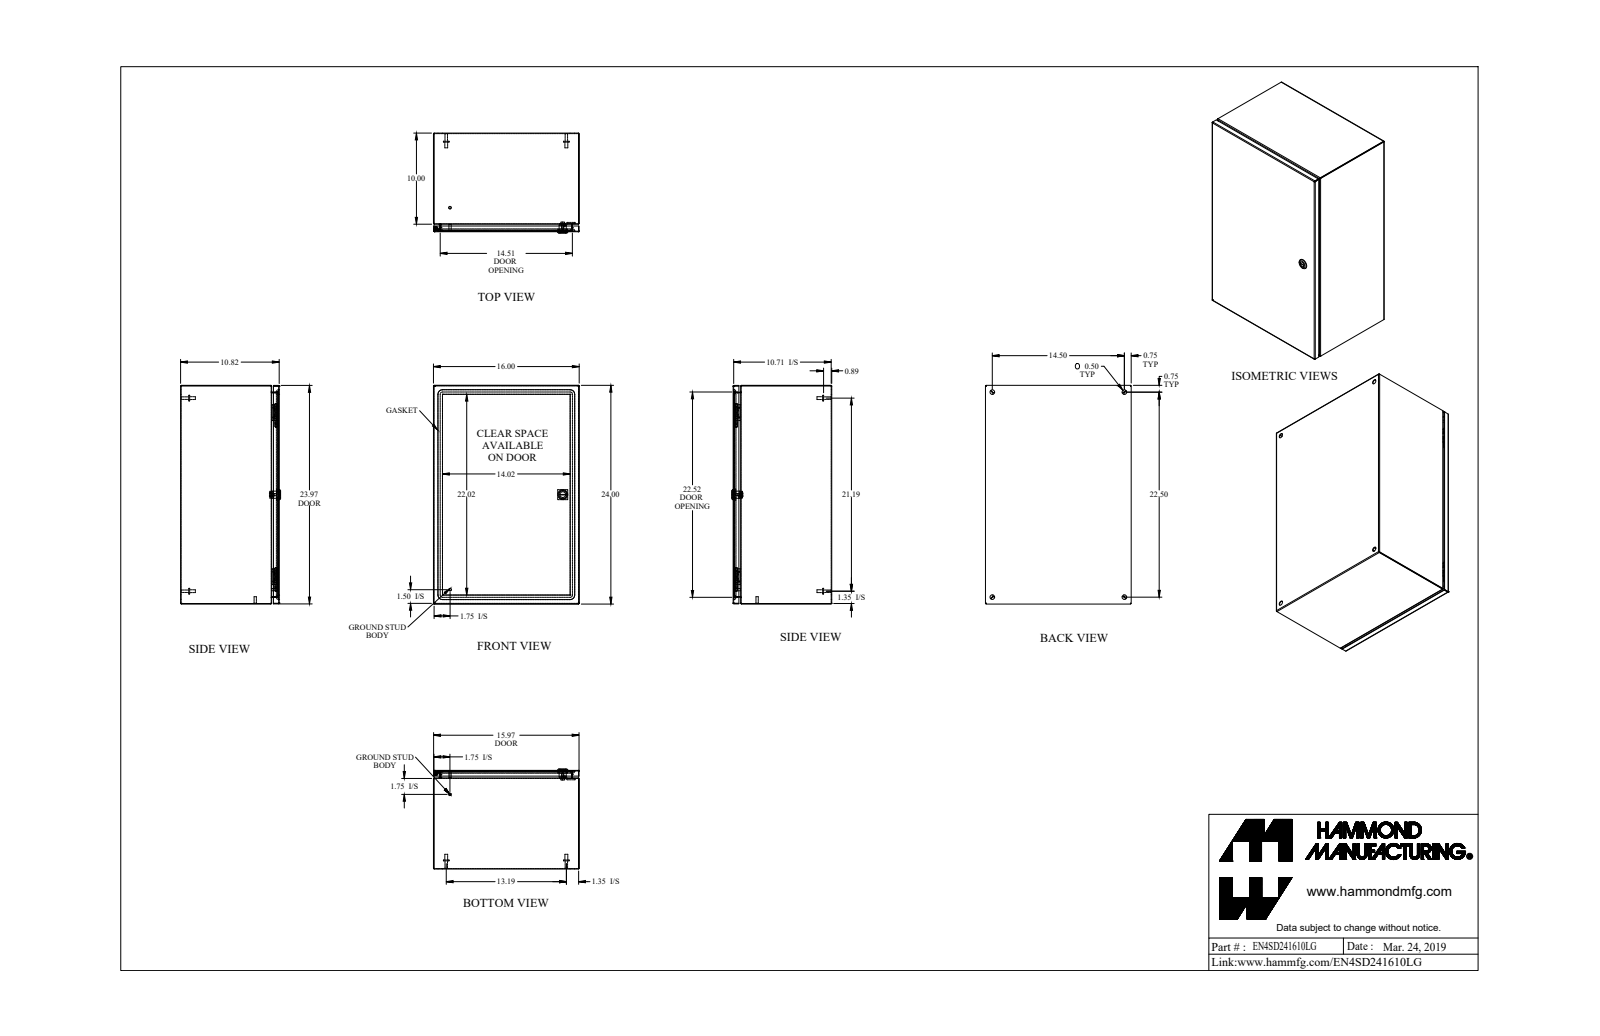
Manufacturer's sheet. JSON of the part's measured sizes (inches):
{"part_name": "EN4SD241610LG_Default", "step_written_by": "SolidWorks 2019 (CONFIG_CONTROL_DESIGN)", "units": "inches", "bodies": {"solids": 21, "faces": 634, "planar": 285, "cylindrical": 213, "other": 136}, "overall_size": [24, 16, 10.982], "volume_in3": 106.1, "surface_area_in2": 3623, "round_holes": [[0.5, 4], [0.172, 1], [0.232, 1], [0.24, 1], [0.242, 1], [0.625, 1], [0.785, 1]], "round_bosses_or_shafts": [[0.625, 4], [0.313, 4], [0.27, 4], [0.281, 2], [0.25, 2], [1.1, 1], [0.525, 1], [0.455, 1]], "partial_cylinders_radius": [[0.029, 21], [0.086, 21], [0.25, 16], [19, 8], [0.006, 4], [0.062, 4], [0.499, 4], [0.125, 2]], "face_to_face_distances": [0.057, 10.765, 15.943, 10.708, 10.822, 23.943, 15.886, 16, 23.886, 24], "hole_center_spacings": [14.5, 22.5, 26.767, 11.299, 11.3, 17.528, 17.528]}
